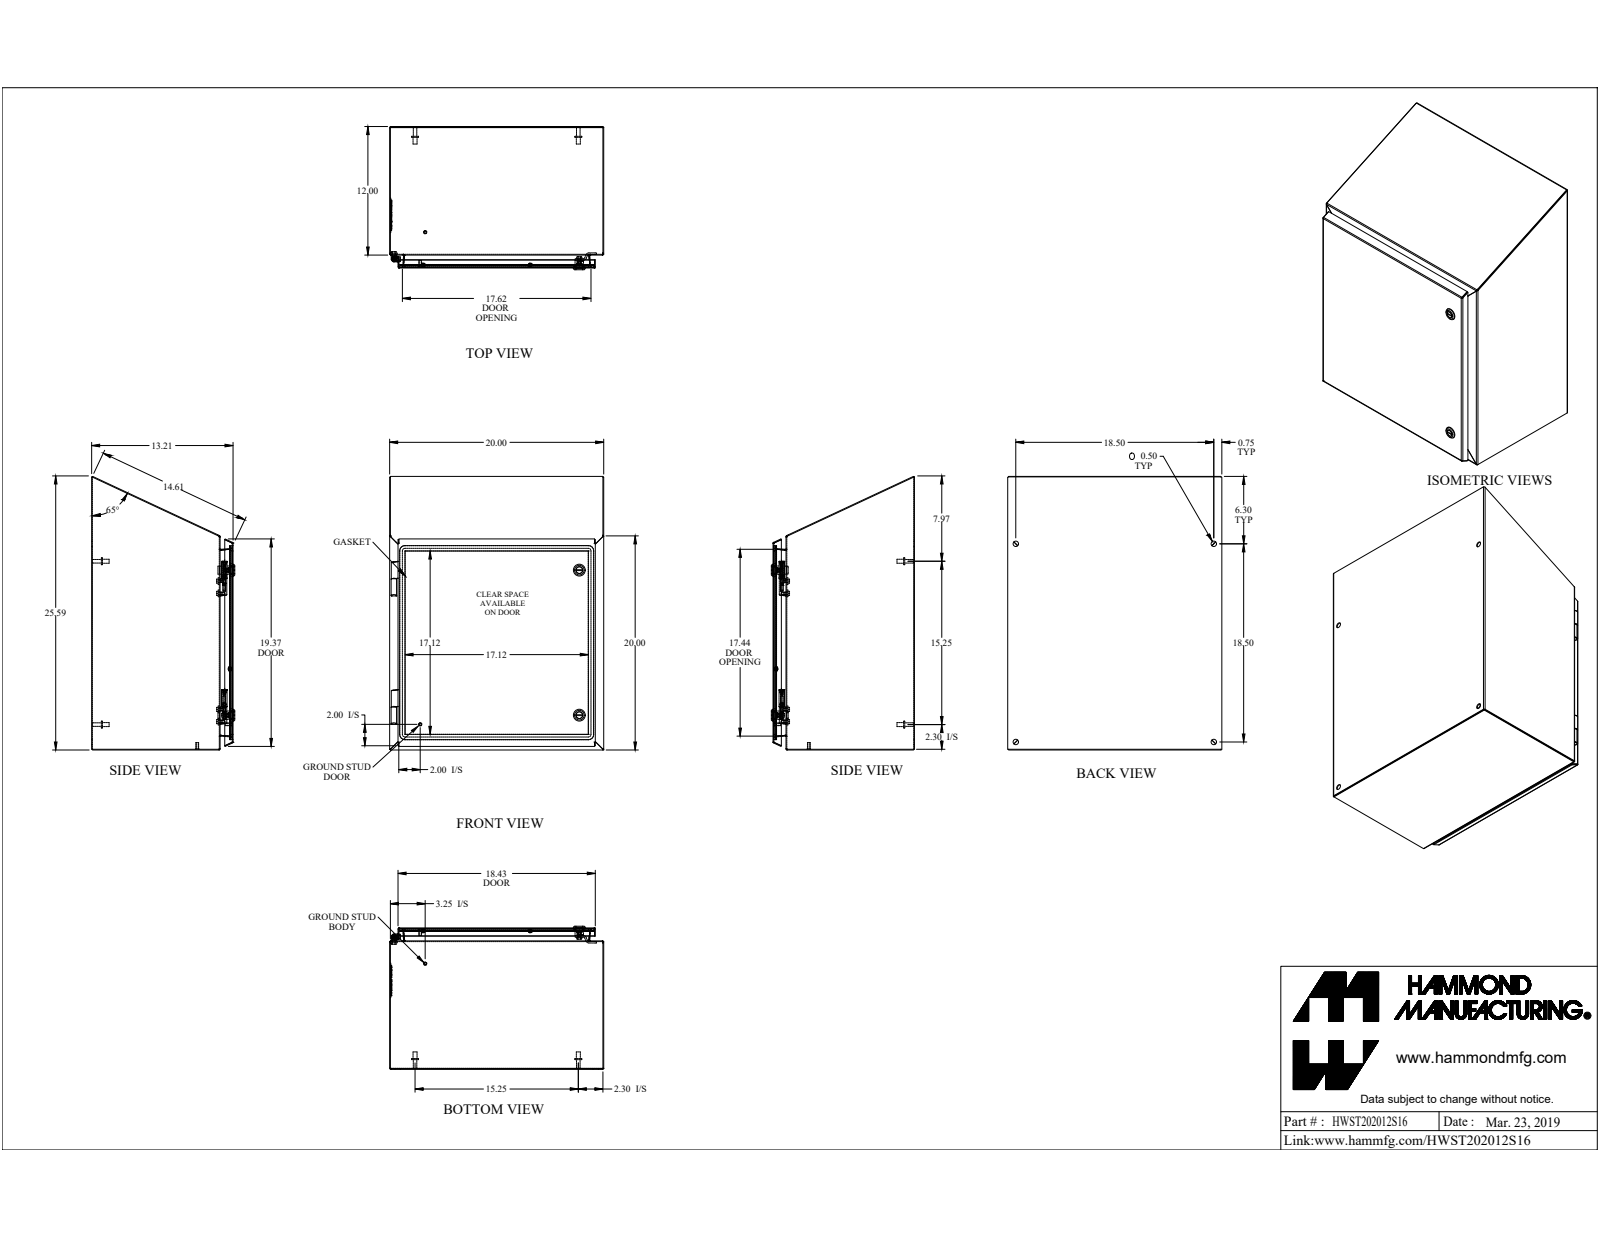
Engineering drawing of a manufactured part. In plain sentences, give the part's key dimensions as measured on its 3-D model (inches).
The part is named "HWST202012S16". Its 3-D file was written by "SolidWorks 2019 (AUTOMOTIVE_DESIGN)". It is 44 solids with 1103 faces: 659 planar, 286 cylindrical and 158 other. Overall it measures 25.545 by 20 by 13.37 inches. Its volume is 170.3 cubic inches and its surface area 4 621 square inches. Round holes: 8 of diameter 0.24, 6 of diameter 0.5, 4 of diameter 0.194, 4 of diameter 0.194, 4 of diameter 0.275, 2 of diameter 0.13, 2 of diameter 0.197, 2 of diameter 0.387, 2 of diameter 0.63, 2 of diameter 0.768, 1 of diameter 0.24, 1 of diameter 3.5. Round bosses or shafts: 8 of diameter 0.226, 4 of diameter 0.65, 4 of diameter 0.625, 4 of diameter 0.375, 4 of diameter 0.332, 4 of diameter 0.25, 3 of diameter 0.236, 2 of diameter 1.1. Partial cylindrical surfaces (rounded edges, fillets, slot ends): 24 of radius 0.25, 18 of radius 0.036, 18 of radius 0.108, 16 of radius 0.039, 12 of radius 0.012, 12 of radius 0.125, 6 of radius 0.03, 6 of radius 0.133. The main face-to-face distances are 0.072, 19.928, 13.066, 13.138, 0.072, 13.138, 13.21, 19.856, 20, 11.928. The hole center spacings are 1.142, 11.974, 18.5, 10.833, 11.979, 13.116, 15.146, 17.354.
